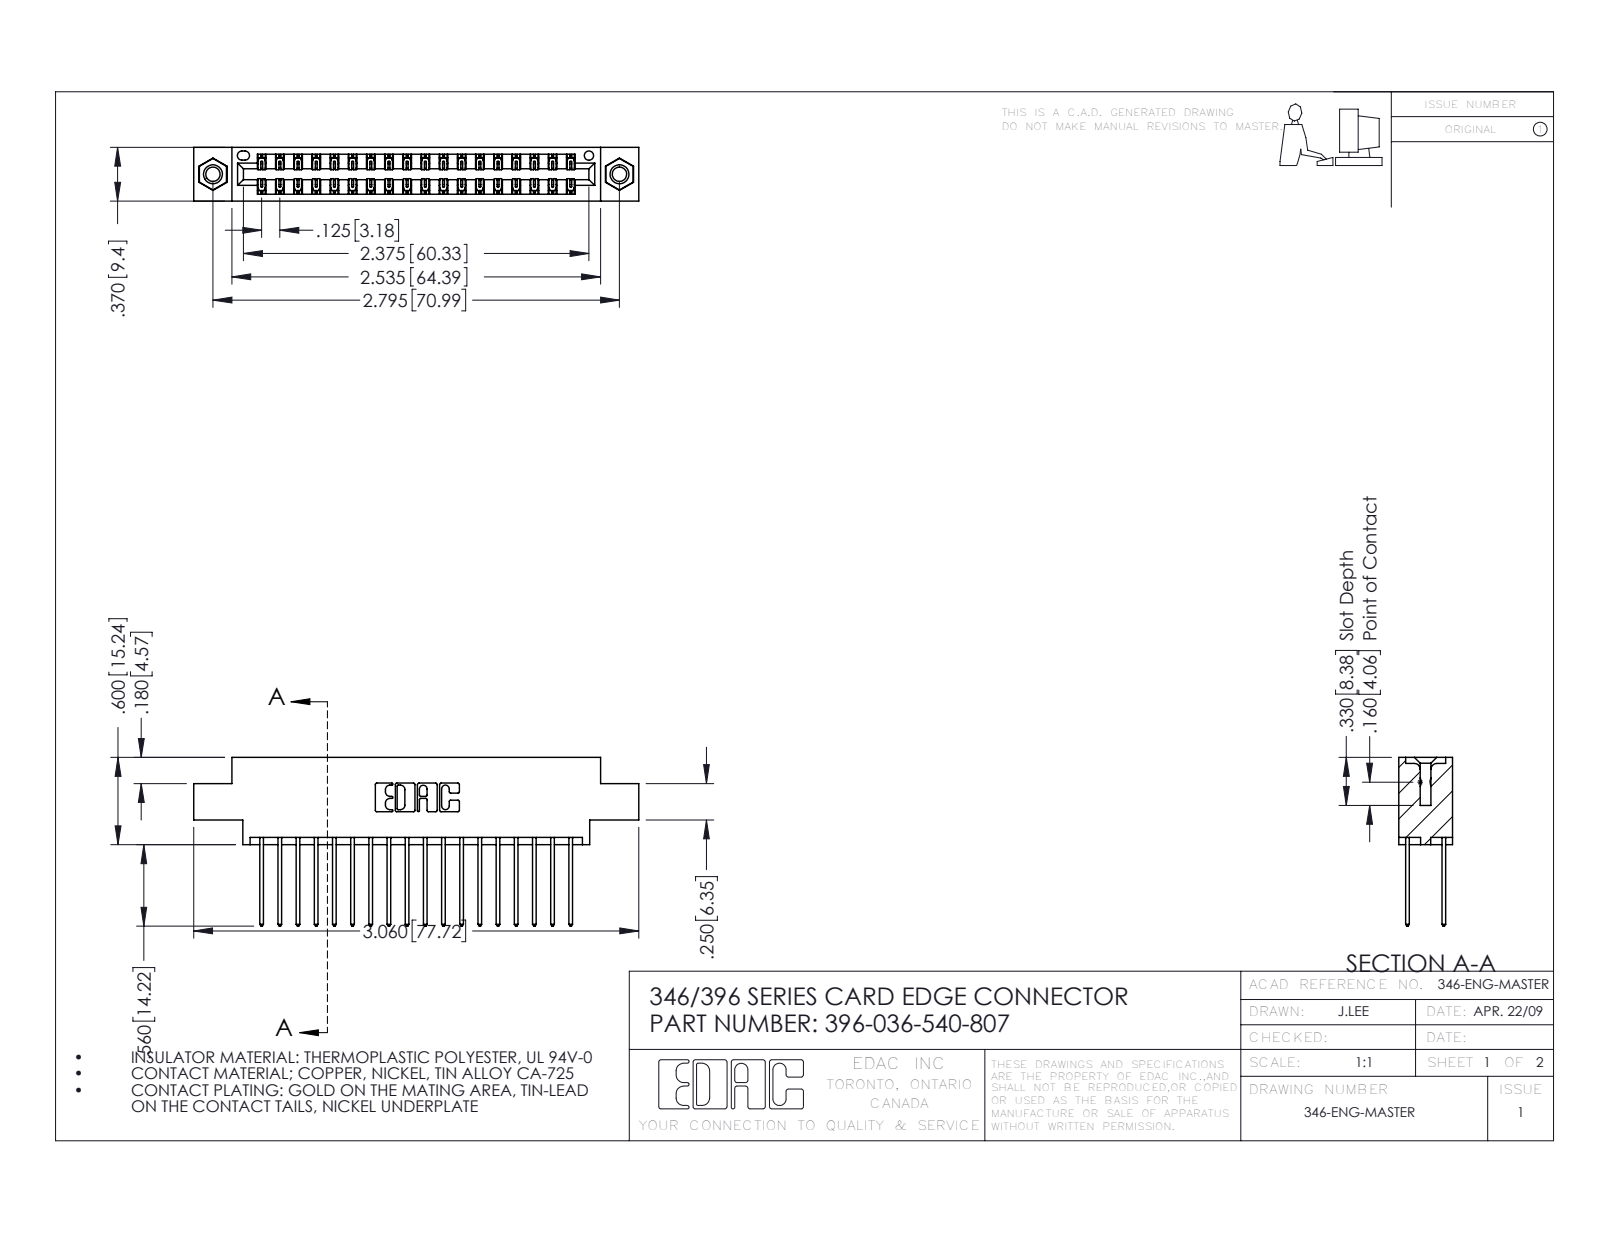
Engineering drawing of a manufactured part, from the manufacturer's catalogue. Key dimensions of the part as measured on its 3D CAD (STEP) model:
Part name (STEP PRODUCT): 346 Part_0.170 Offset - 0.156 Dia-TI; 396-036-540-807; 345-292-001_345-293-140; 345-250-001_345-250-005-103
STEP written by: SolidWorks 2016 (CONFIG_CONTROL_DESIGN)
Units: inches
Bodies: 39 solids, 2058 faces (1372 planar, 670 cylindrical, 16 other)
Overall size (bounding box): 3.06 × 1.16 × 0.37
Volume: 0.449 in³ · Surface area: 16.43 in²
Round holes (diameter × count): ⌀0.098 ×2, ⌀0.125 ×2, ⌀0.156 ×2, ⌀0.064 ×1
Round bosses / shafts (diameter × count): ⌀0.155 ×2
Partial cylindrical surfaces — rounded edges, fillets, slot ends (radius × count): R0.006 ×54, R0.01 ×36, R0.01 ×22, R0.007 ×6, R0.031 ×6, R0.026 ×3, R0.014 ×2, R0.022 ×2
Main face-to-face distances: 0.048, 0.322, 0.25, 0.37, 0.072, 0.298, 0.025, 0.275, 0.222, 0.148
Hole centre spacings: 0.246, 2.588, 2.795
